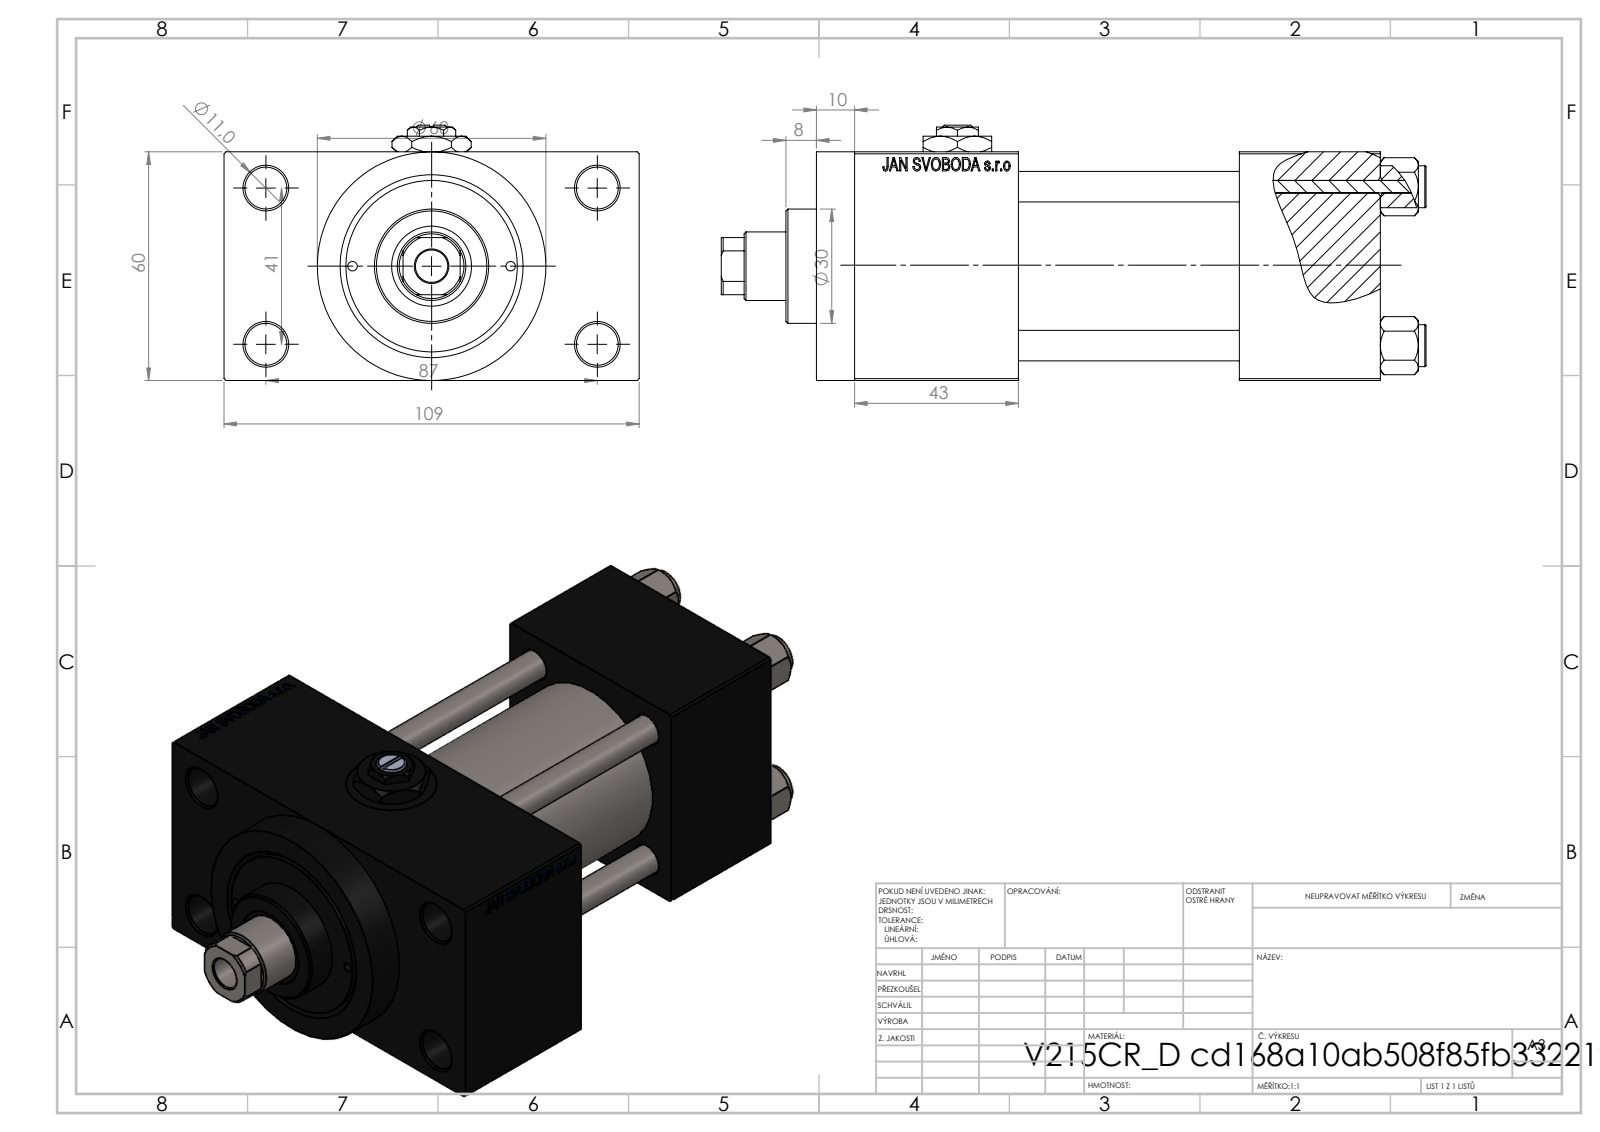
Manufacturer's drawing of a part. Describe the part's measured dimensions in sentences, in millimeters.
The part is named "V215CR_D_Body; NUT_M5_D; V215CR_VCP_D; Zatka_pro_OIL_PORT (+2 more)". Its 3-D file was written by "SolidWorks 2019 (CONFIG_CONTROL_DESIGN)". It is 12 solids with 1160 faces: 524 planar, 96 cylindrical and 540 other. Overall it measures 185 by 109 by 67 millimeters. Its volume is 511 877 cubic millimeters and its surface area 123 415 square millimeters. Round holes: 4 of diameter 8, 4 of diameter 11, 3 of diameter 16.66, 3 of diameter 24, 2 of diameter 2.5, 2 of diameter 7, 1 of diameter 8.5, 1 of diameter 18, 1 of diameter 21, 1 of diameter 31, 1 of diameter 40, 1 of diameter 45. Round bosses or shafts: 4 of diameter 11, 1 of diameter 60, 1 of diameter 46, 1 of diameter 30. Partial cylindrical surfaces (rounded edges, fillets, slot ends): 1 of radius 8.5. The main face-to-face distances are 60, 58, 24.5, 84.5, 37, 95, 43, 138, 101, 10. The hole center spacings are 20.85, 22.65, 29.49, 30.62, 41.7, 46.53, 47.15, 48.09.
